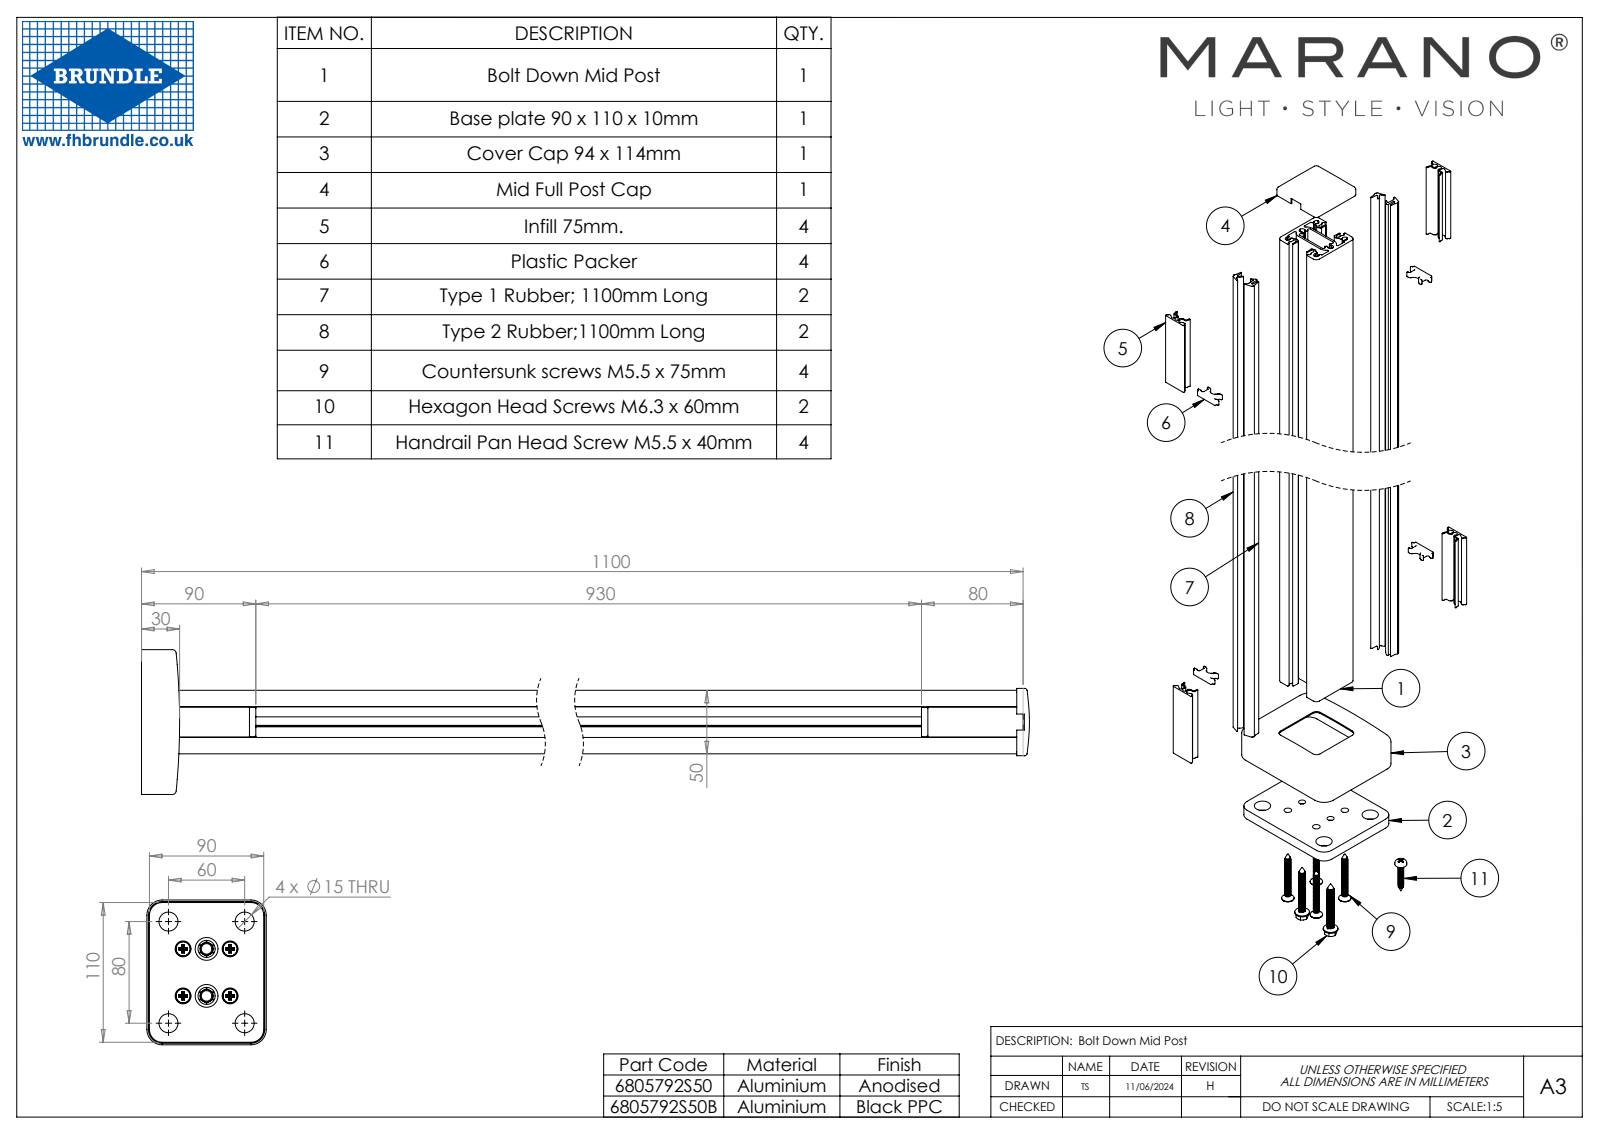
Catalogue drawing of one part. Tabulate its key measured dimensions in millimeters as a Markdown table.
| quantity | value |
| --- | --- |
| part name | 6805792S50 Part1; 680520750; hexagon head tapping screws with collar gb_GB_SQUARE_AND_HEXAGON_TYPE136 ST6.3X50 C-S; 6805792S50 (+7 more) |
| STEP written by | SolidWorks 2020 (CONFIG_CONTROL_DESIGN) |
| units | millimeters |
| bodies | 22 solids, 2570 faces (536 planar, 1142 cylindrical, 892 other) |
| overall size | 1104.98 × 114 × 94 |
| volume | 1 293 000 mm³ |
| surface area | 965 905 mm² |
| round holes (diameter × count) | 7 × 4, 12.5 × 4, 15 × 4, 6.5 × 2, 8.33 × 2, 18 × 2 |
| round bosses / shafts (diameter × count) | 11.5 × 4, 5.5 × 4, 13.5 × 2, 6.3 × 2 |
| partial cylindrical surfaces (radius × count) | 0.5 × 176, 1 × 34, 3 × 20, 0.3 × 14, 1.5 × 12, 0.6 × 10, 1.6 × 8, 2 × 8 |
| main face-to-face distances | 16, 18, 50, 2, 32, 34, 3, 47, 14, 3.25 |
| hole center spacings | 37, 18.5, 24.38, 36.91, 41.37, 53.05, 59.62, 65.74 |
